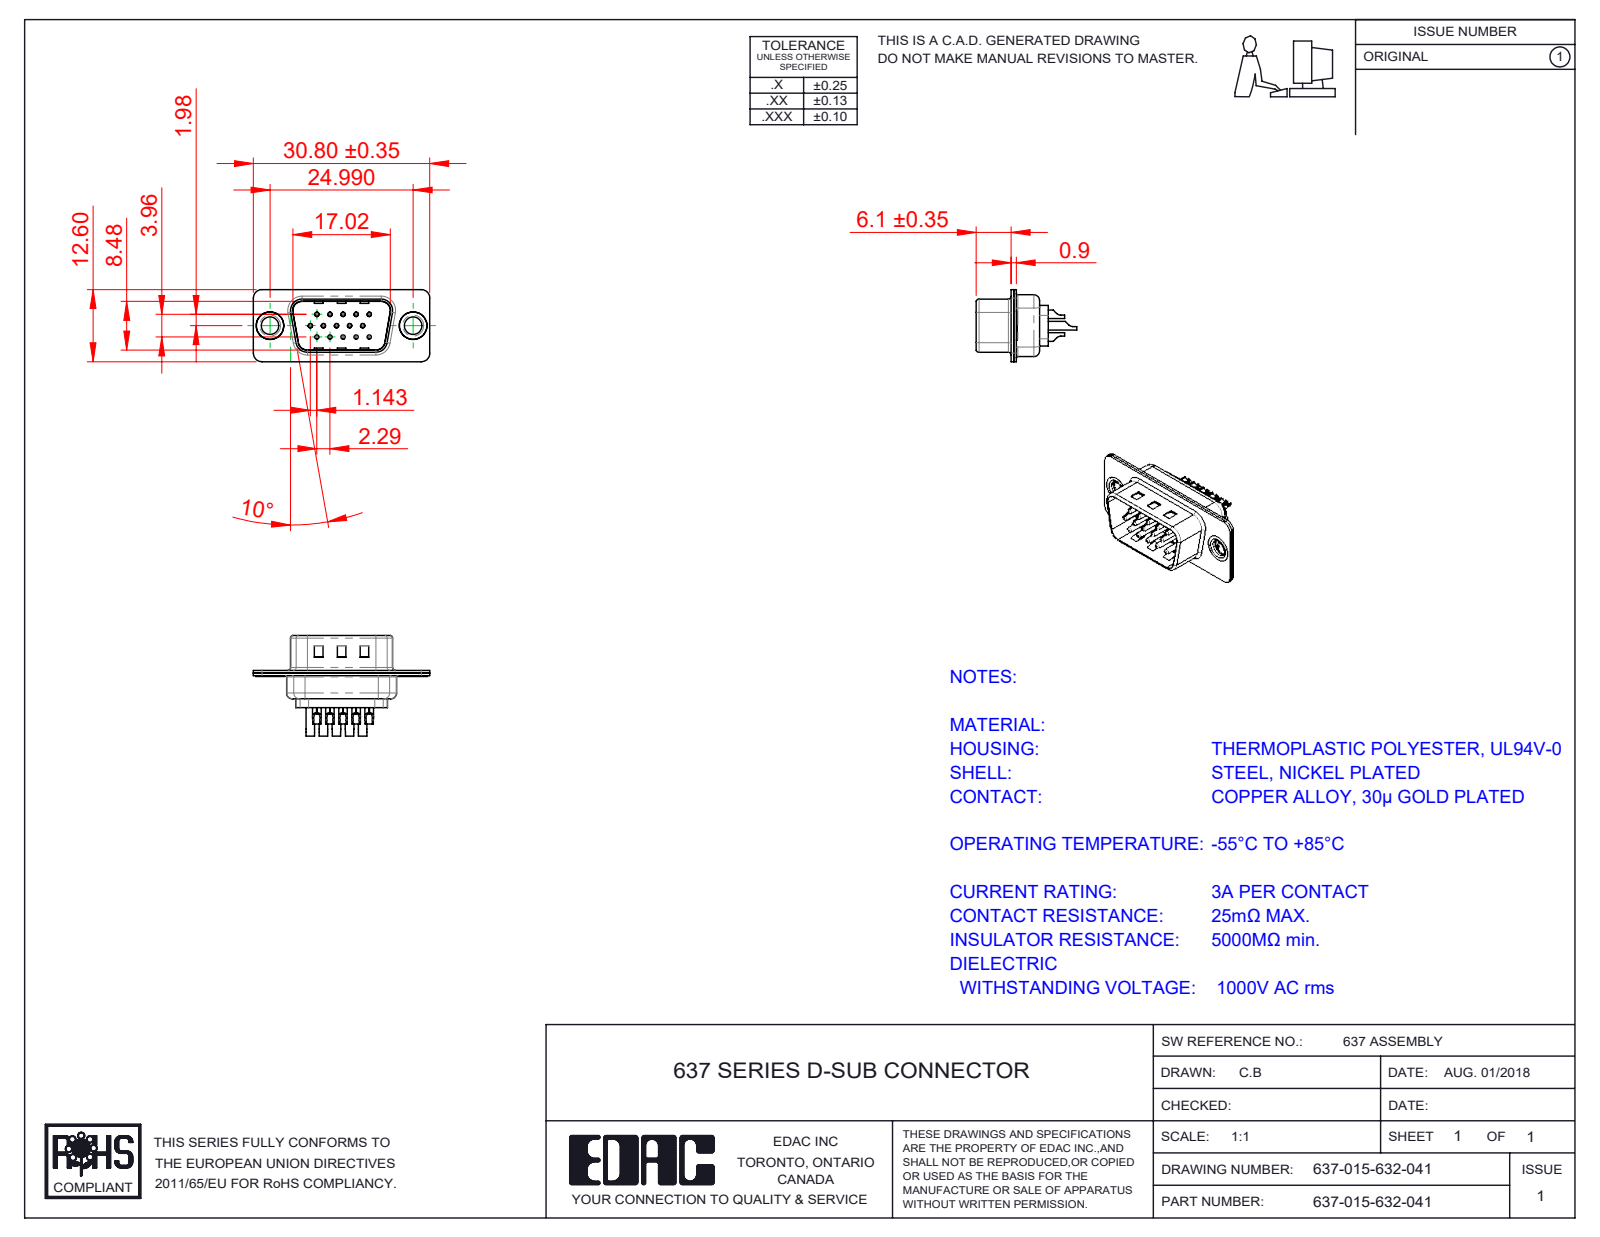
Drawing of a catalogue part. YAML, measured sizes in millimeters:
part_name: "637 Shell Front_15 Contacts; 637 Contact Row 1_32; 637 Contact Row 3_32; 637 Shell Rear_15 Contacts (+4 more)"
step_written_by: "SolidWorks 2020 (CONFIG_CONTROL_DESIGN)"
units: millimeters
bodies: {solids: 20, faces: 1238, planar: 317, cylindrical: 548, other: 373}
overall_size: [30.8, 17.55, 12.6]
volume: 1253
surface_area: 4633
round_holes:
  - {diameter: 0.35, count: 15}
  - {diameter: 1.1, count: 15}
  - {diameter: 1.6, count: 15}
  - {diameter: 3.05, count: 2}
  - {diameter: 4, count: 2}
  - {diameter: 4.8, count: 2}
round_bosses_or_shafts:
  - {diameter: 2, count: 15}
  - {diameter: 1.5, count: 15}
  - {diameter: 0.75, count: 15}
  - {diameter: 5, count: 2}
  - {diameter: 4.9, count: 2}
  - {diameter: 3.55, count: 2}
partial_cylinders:
  - {radius: 1.5, count: 16}
  - {radius: 2, count: 12}
  - {radius: 0.5, count: 8}
  - {radius: 1, count: 7}
  - {radius: 0.25, count: 4}
  - {radius: 0.55, count: 4}
  - {radius: 0.7, count: 4}
  - {radius: 0.95, count: 4}
face_to_face_distances: [0.45, 0.9, 0.4, 0.7, 8.88, 1.05, 8.48, 0.31, 4.55, 1.16]
hole_center_spacings: [3.96, 2.28, 4.57, 2.29, 6.05, 6.86, 7.92, 6.04]
